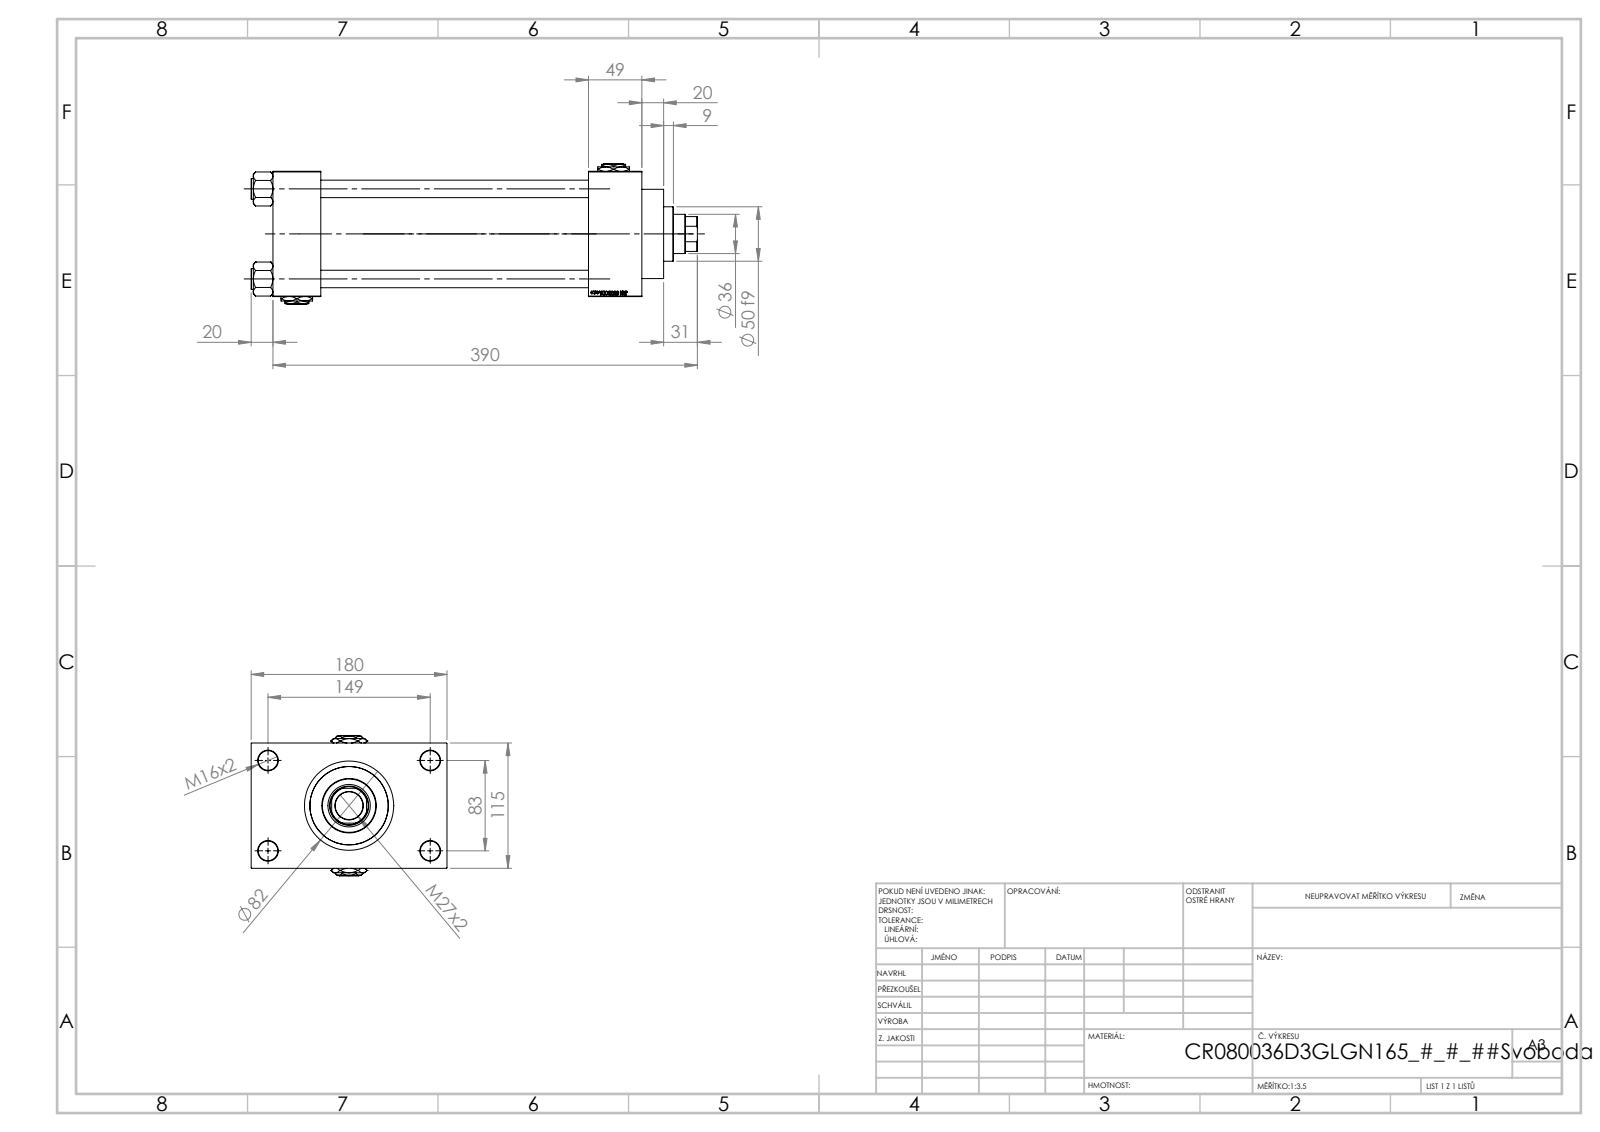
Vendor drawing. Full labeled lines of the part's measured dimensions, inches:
Part name (STEP PRODUCT): V215CR_D_Body; V215CR_D_TYCINKA; V215_VC_A; Zatka_pro_OIL_PORT (+2 more)
STEP written by: SolidWorks 2019 (CONFIG_CONTROL_DESIGN)
Units: inches
Bodies: 13 solids, 1236 faces (589 planar, 89 cylindrical, 558 other)
Overall size (bounding box): 16.142 × 7.087 × 5.079
Volume: 151 in³ · Surface area: 694.9 in²
Round holes (diameter × count): ⌀0.63 ×4, ⌀0.709 ×4, ⌀0.276 ×2, ⌀1.041 ×2, ⌀1.378 ×2, ⌀1.004 ×1, ⌀1.417 ×1, ⌀1.535 ×1, ⌀2.402 ×1, ⌀2.835 ×1, ⌀3.15 ×1
Round bosses / shafts (diameter × count): ⌀0.748 ×4, ⌀3.386 ×1, ⌀3.228 ×1, ⌀1.969 ×1
Partial cylindrical surfaces — rounded edges, fillets, slot ends (radius × count): R0.689 ×1
Main face-to-face distances: 4.528, 9.685, 11.614, 1.929, 1.732, 11.417, 13.346, 1.28, 5.807, 7.087
Hole centre spacings: 1.305, 2.302, 3.256, 3.357, 3.513, 4.561, 5.607, 3.268
